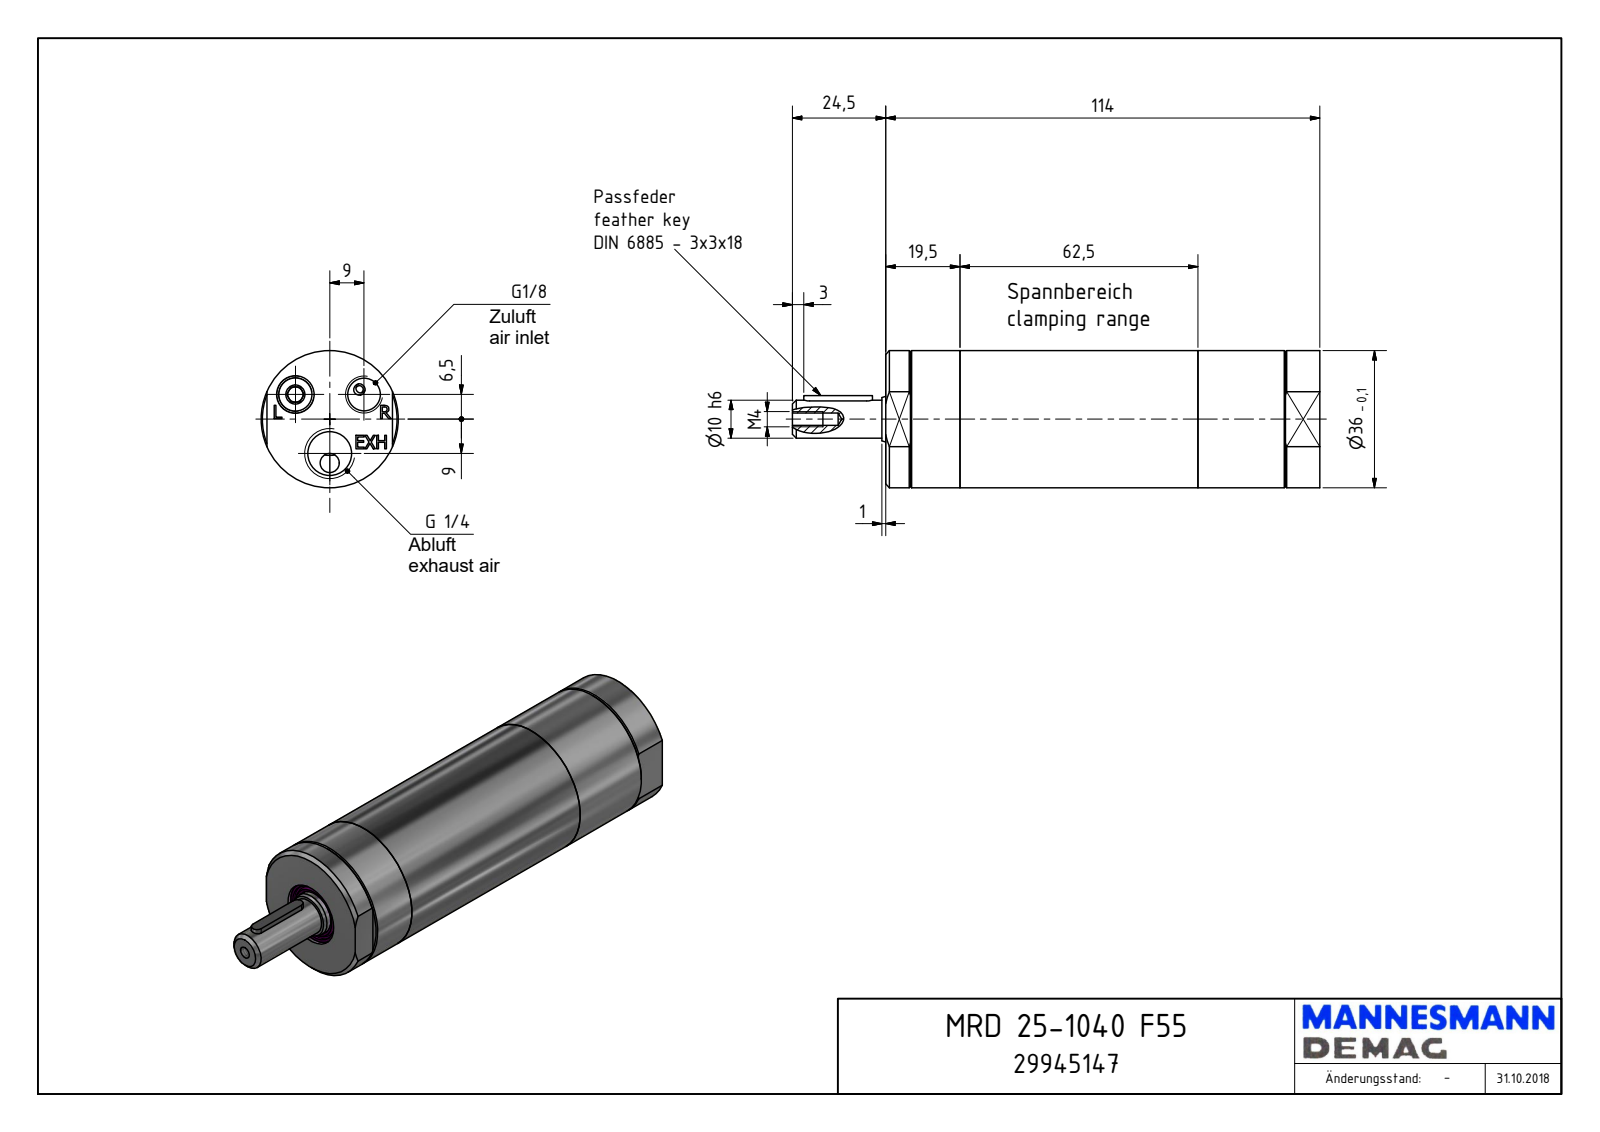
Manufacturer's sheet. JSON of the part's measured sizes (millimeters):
{"part_name": "MRD 25-1040_29945147", "step_written_by": "Autodesk Inventor 2018 (AUTOMOTIVE_DESIGN)", "units": "millimeters", "bodies": {"solids": 1, "faces": 143, "planar": 95, "cylindrical": 20, "other": 28}, "overall_size": [138.5, 36, 36], "volume_mm3": 115530, "surface_area_mm2": 16953, "round_holes": [[8.57, 2], [3.24, 1], [4, 1], [11.45, 1], [15.5, 1], [17, 1]], "round_bosses_or_shafts": [[36, 1], [11.95, 1], [10, 1]], "partial_cylinders_radius": [[1.5, 2], [16.55, 1]], "face_to_face_distances": [114, 104.43, 9.57, 33, 1, 106, 105, 1.57, 8, 15], "hole_center_spacings": [11.1, 17.92, 9, 18]}
